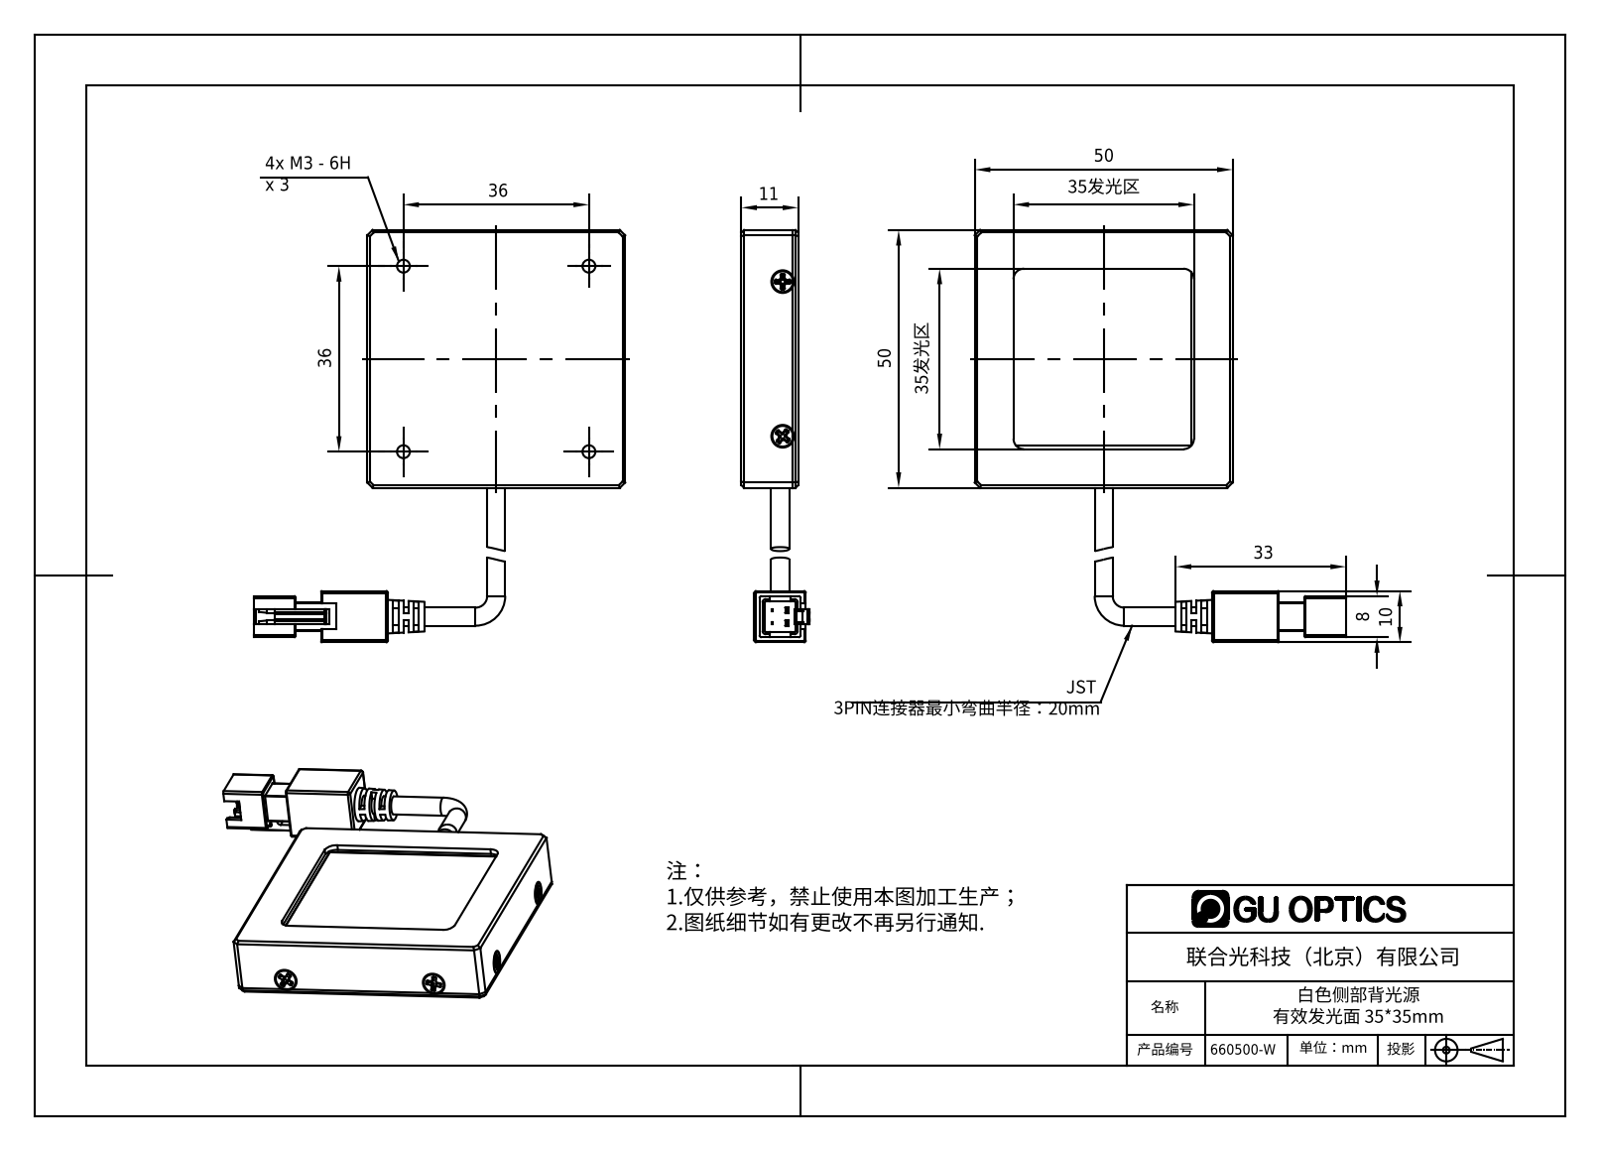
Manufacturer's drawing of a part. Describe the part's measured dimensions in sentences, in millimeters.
The part is named "660500-W". Its 3-D file was written by "SolidWorks 2016 (AUTOMOTIVE_DESIGN)". It is 37 solids with 955 faces: 540 planar, 232 cylindrical and 183 other. Overall it measures 80.2 by 72 by 13.2 millimeters. Its volume is 23 999 cubic millimeters and its surface area 35 401 square millimeters. Round holes: 4 of diameter 1.6, 4 of diameter 2.4, 4 of diameter 2.5, 1 of diameter 3.6. Round bosses or shafts: 4 of diameter 2, 2 of diameter 3.5. Partial cylindrical surfaces (rounded edges, fillets, slot ends): 109 of radius 0.2, 15 of radius 0.1, 12 of radius 0.4, 7 of radius 1, 4 of radius 2, 1 of radius 0.3, 1 of radius 0.68, 1 of radius 1.4. The main face-to-face distances are 4.2, 1, 5.5, 4.1, 1.2, 4.5, 4.3, 1.1, 5.3, 4. The hole center spacings are 36, 15.01, 30, 50.91.
